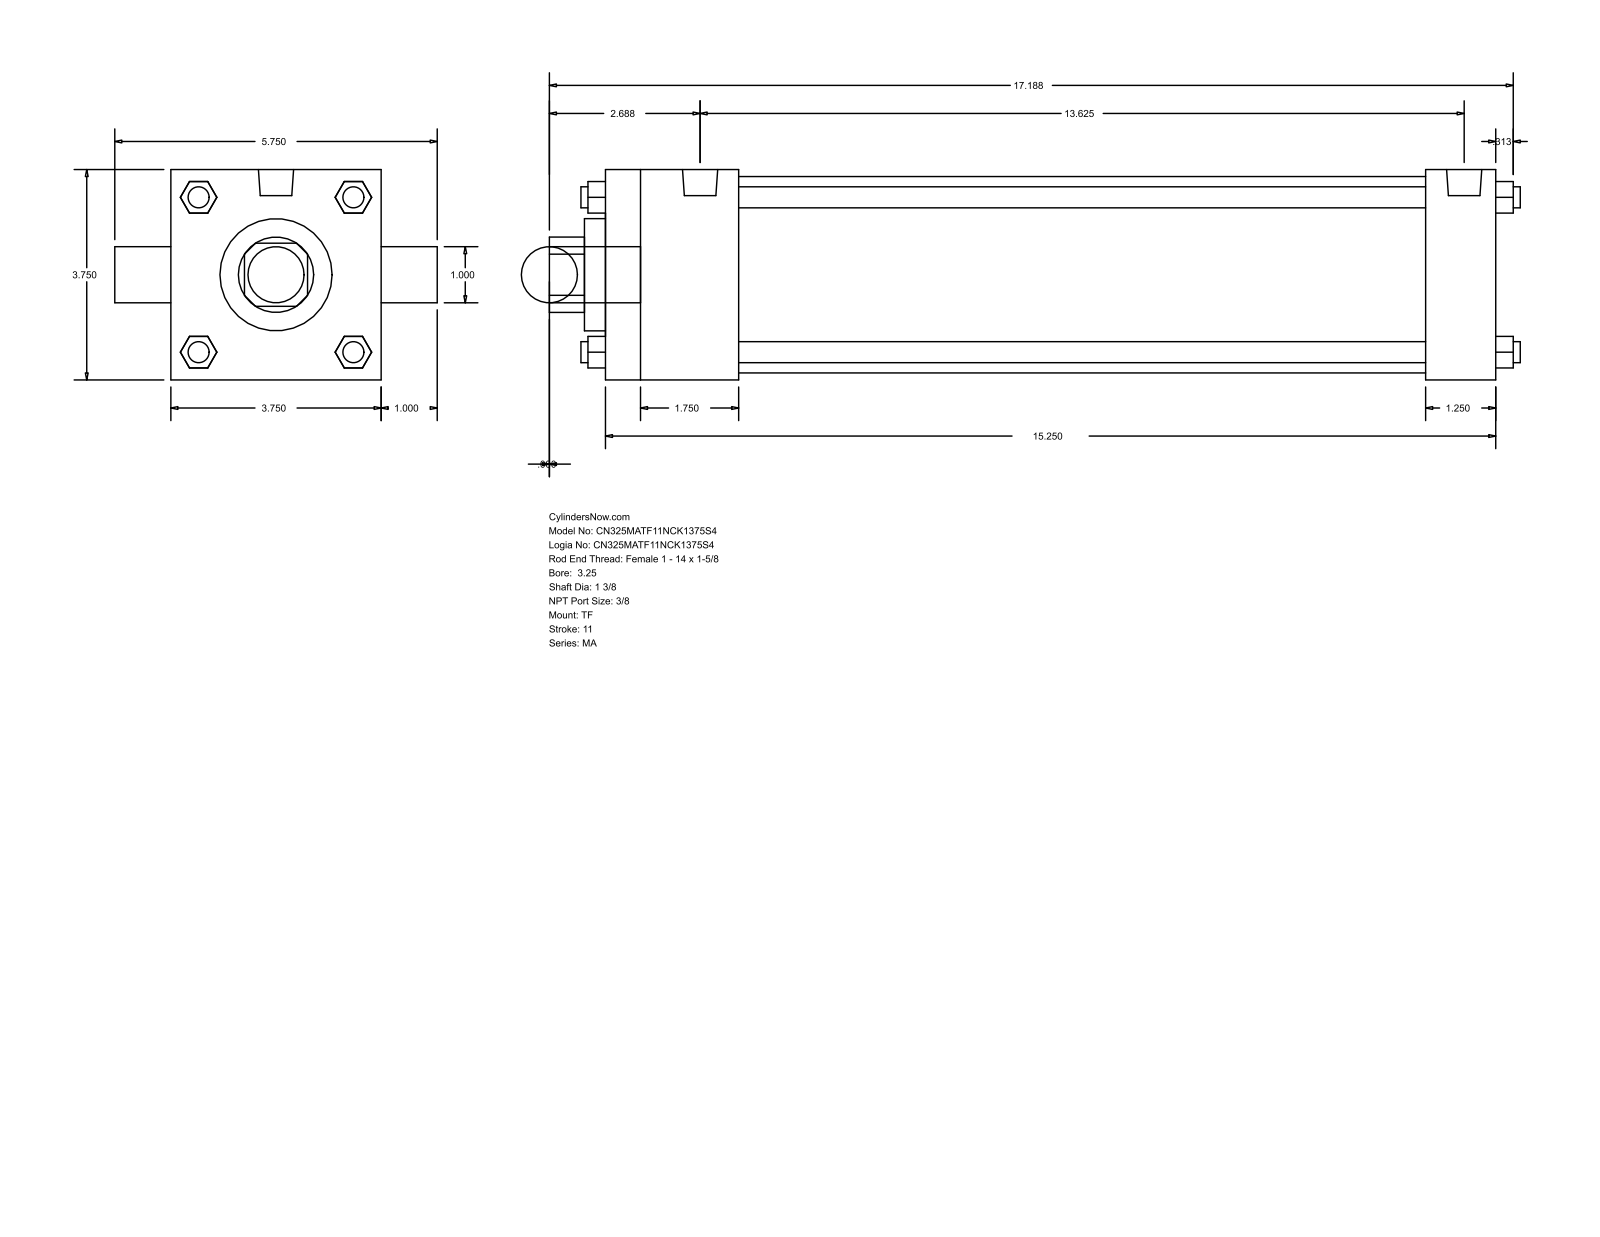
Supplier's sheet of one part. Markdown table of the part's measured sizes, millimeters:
| quantity | value |
| --- | --- |
| part name | MA_TF__0325_1.375 |
| STEP written by | GSSL Pune (CONFIG_CONTROL_DESIGN) |
| units | millimeters |
| bodies | 0 solids, 120 faces (92 planar, 28 cylindrical, 0 other) |
| overall size | 439.74 × 146.05 × 95.25 |
| round holes (diameter × count) | 25.4 × 1, 34.92 × 1, 50.8 × 1, 88.9 × 1 |
| round bosses / shafts (diameter × count) | 9.53 × 4, 11.11 × 3, 15.93 × 2, 25.4 × 1 |
| partial cylindrical surfaces (radius × count) | 17.06 × 1 |
| main face-to-face distances | 95.24, 403.22, 60.32, 371.48, 311.16, 342.9, 31.74, 9.52, 69.84, 381 |
